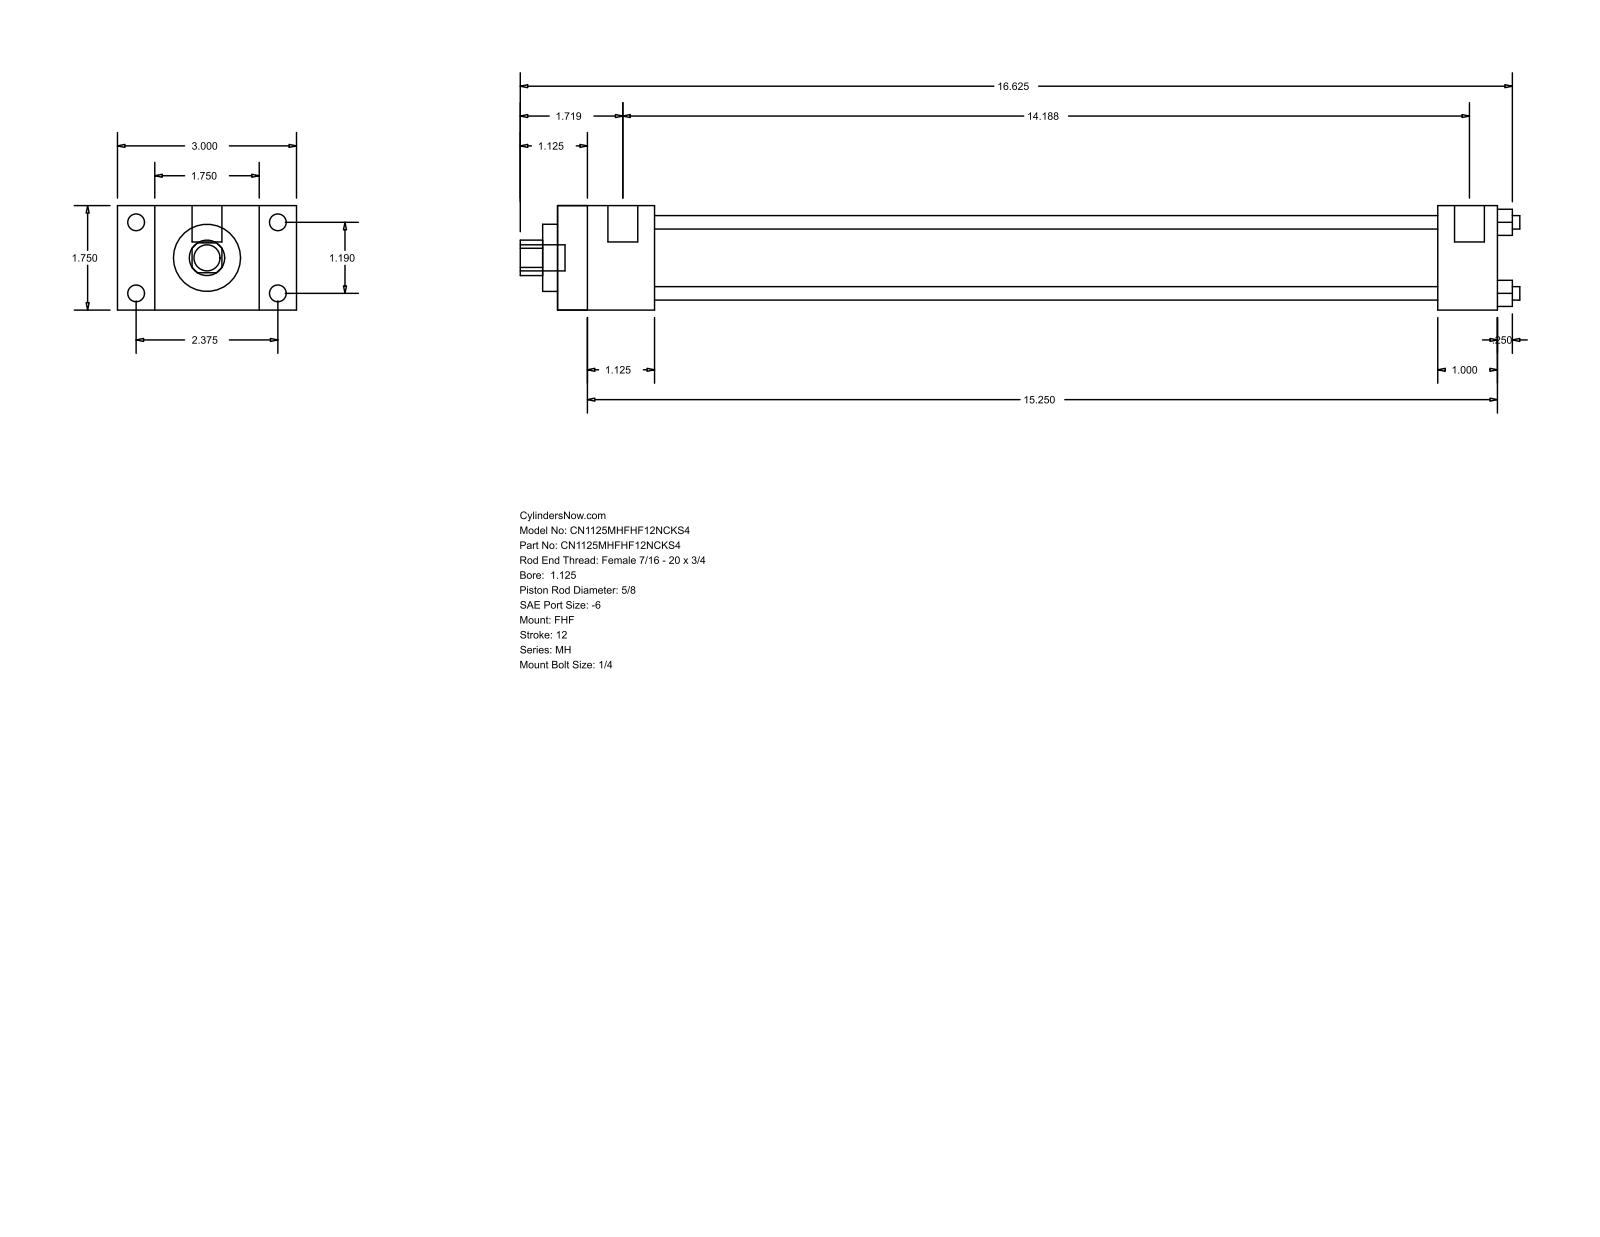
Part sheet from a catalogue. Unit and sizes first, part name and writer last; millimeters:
Units: millimetres
Overall size (bounding box): 425.45 × 76.2 × 44.45
Round holes (diameter × count): ⌀5.71 ×4, ⌀15.88 ×1, ⌀28.57 ×1, ⌀34.92 ×1
Round bosses / shafts (diameter × count): ⌀7.14 ×4, ⌀5.56 ×4, ⌀12.7 ×2, ⌀11.11 ×1
Partial cylindrical surfaces — rounded edges, fillets, slot ends (radius × count): R7.54 ×1
Main face-to-face distances: 44.46, 15.87, 60.33, 41.27, 76.2, 400.05, 358.78, 374.64, 333.37, 25.41
Hole centre spacings: 21.37, 30.22, 42.74
Bodies: 0 solids, 88 faces (60 planar, 28 cylindrical, 0 other)
Part name (STEP PRODUCT): MH_FHF__0112_0.625
STEP written by: GSSL Pune (CONFIG_CONTROL_DESIGN)
